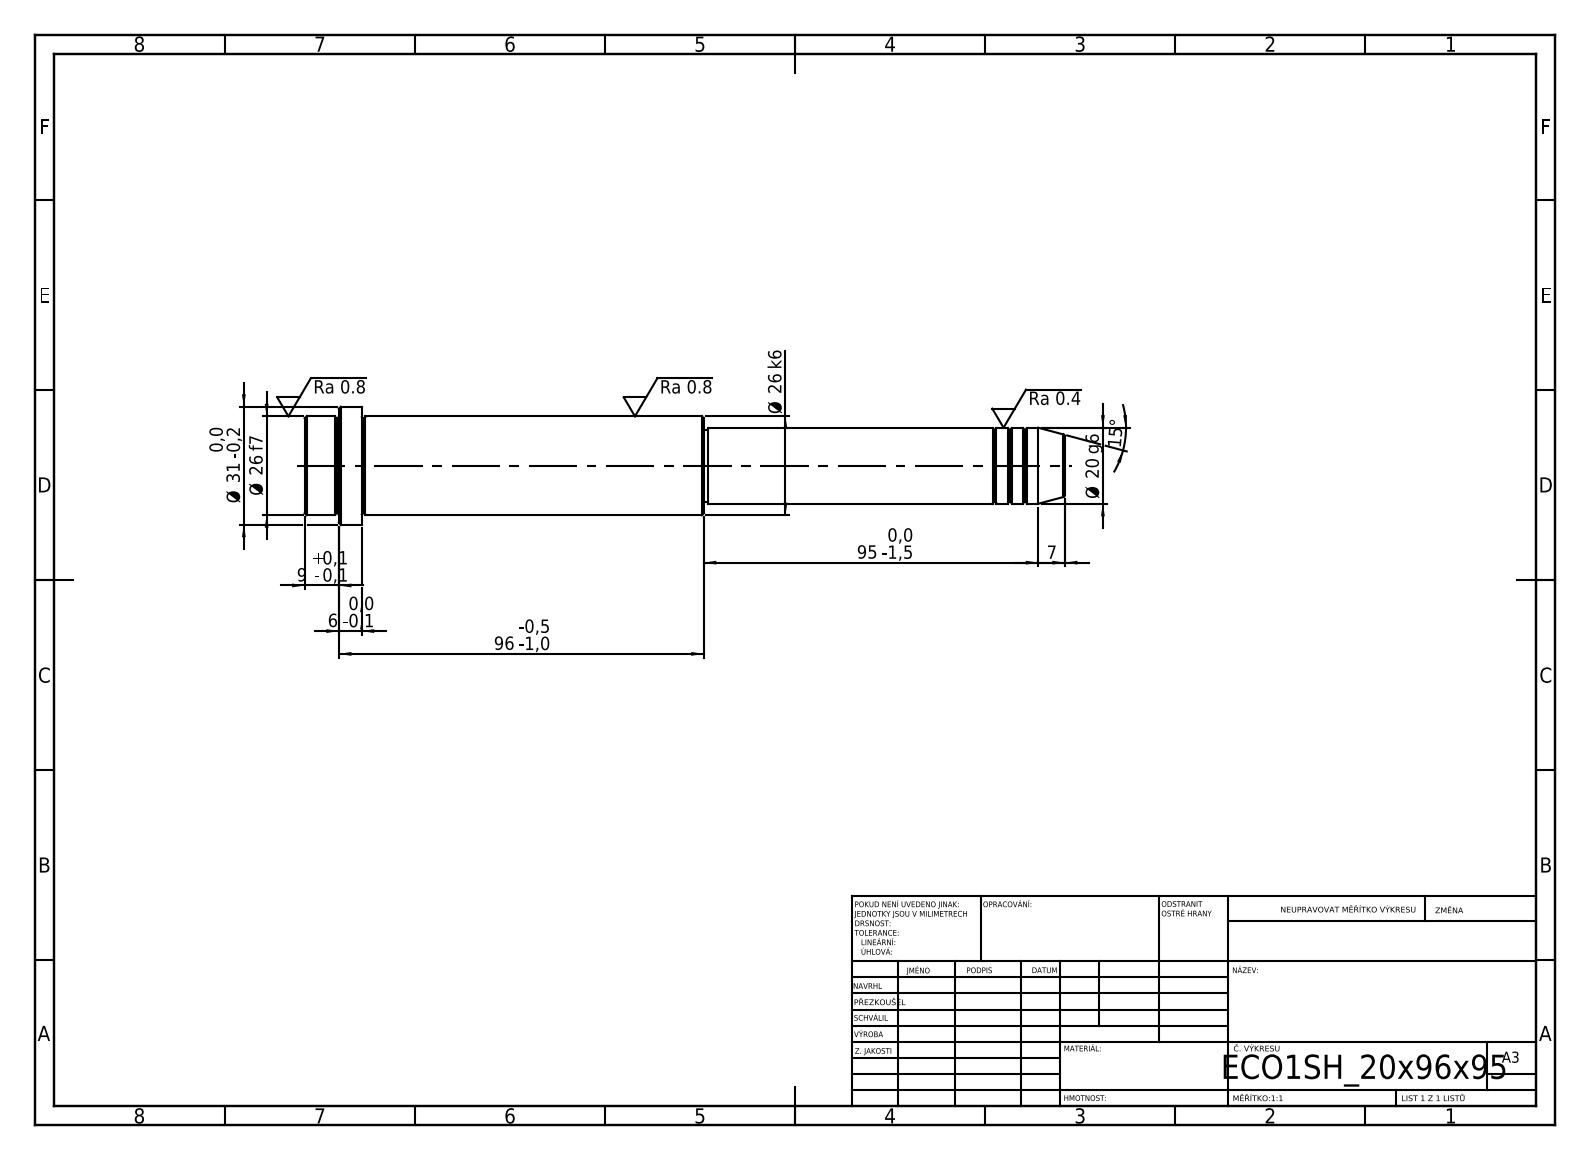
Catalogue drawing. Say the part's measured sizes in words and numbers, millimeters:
Its 3-D file was written by "SolidWorks 2019 (CONFIG_CONTROL_DESIGN)". It is 1 solid with 52 faces: 6 planar, 16 cylindrical and 30 other. Overall it measures 200 by 31 by 31 millimeters. Its volume is 86 349 cubic millimeters and its surface area 16 175 square millimeters. Round bosses or shafts: 1 of diameter 31, 1 of diameter 26, 1 of diameter 20, 1 of diameter 19. The main face-to-face distances are 15, 90, 105, 95, 185, 200, 191, 96, 6, 9.
